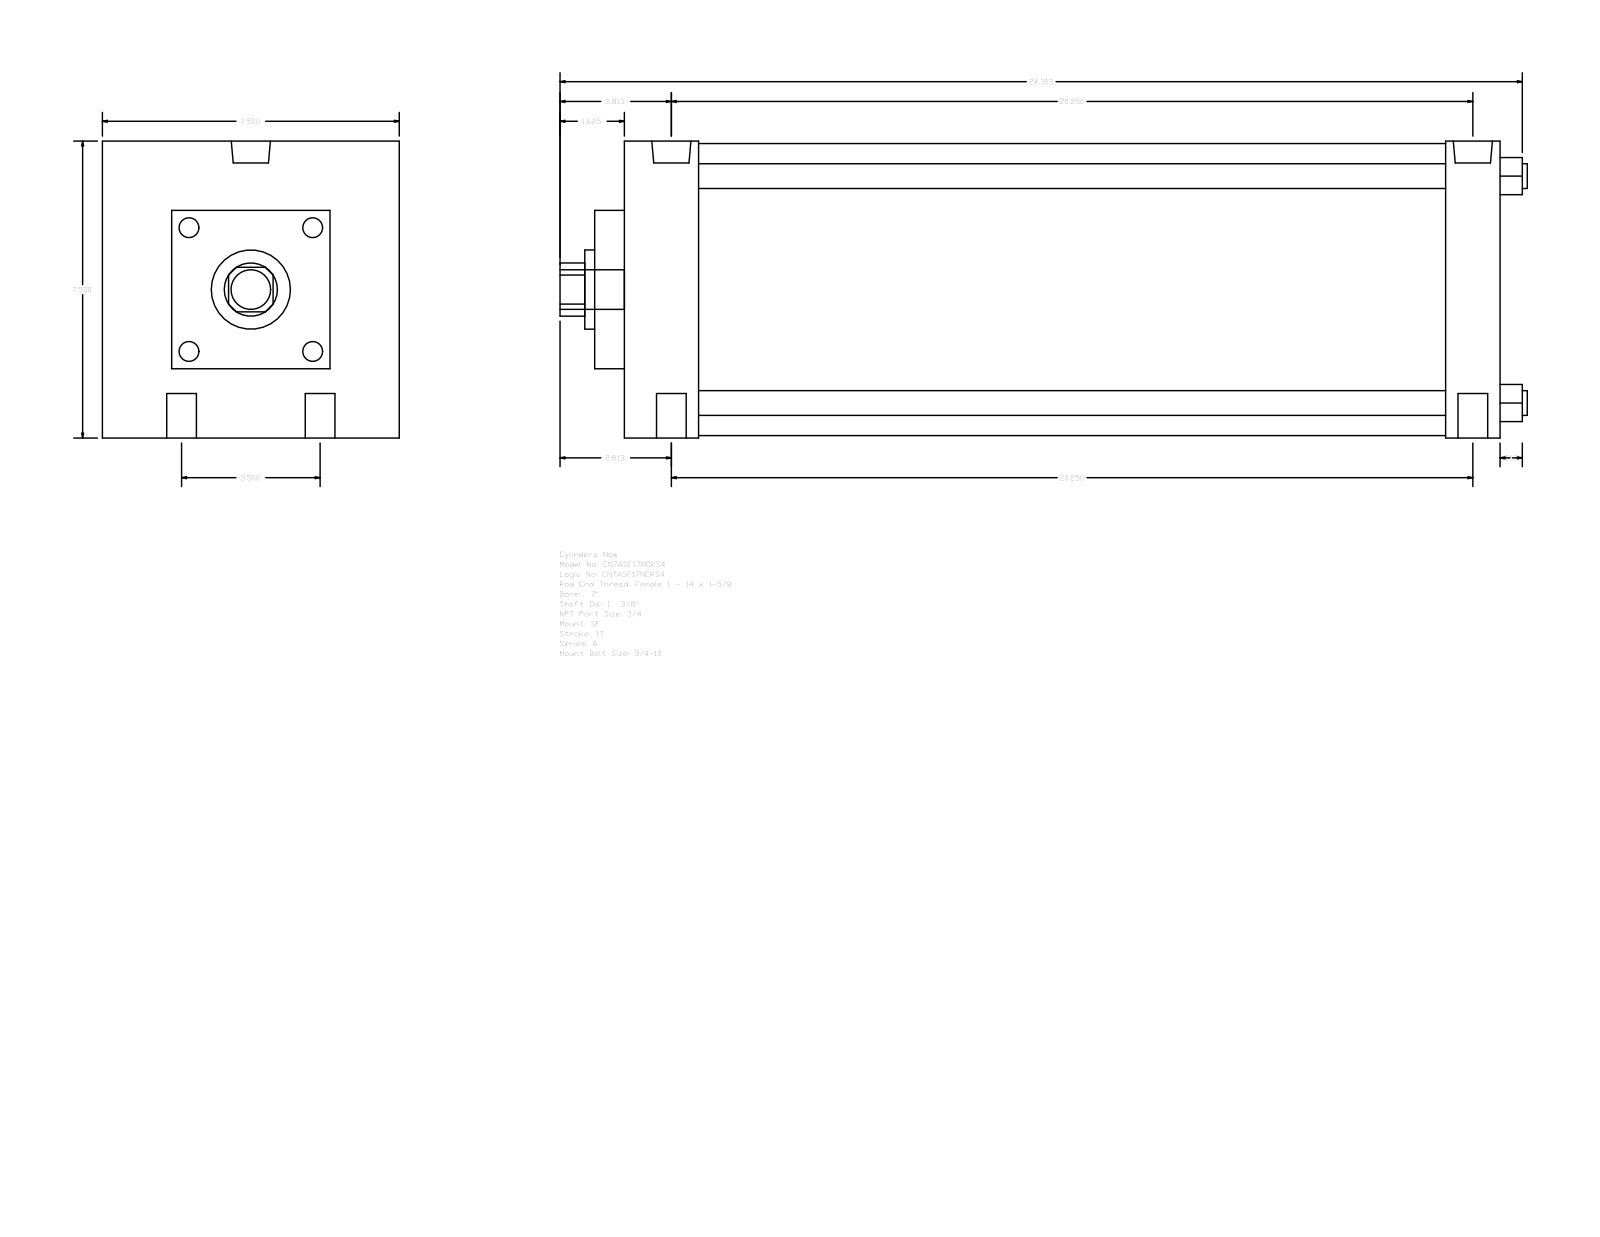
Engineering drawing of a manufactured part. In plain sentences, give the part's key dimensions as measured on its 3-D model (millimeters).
The part is named "A_SF__0700_1.375". Its 3-D file was written by "GSSL Pune (CONFIG_CONTROL_DESIGN)". It is 0 solids with 93 faces: 67 planar, 26 cylindrical and 0 other. Overall it measures 620.71 by 190.5 by 190.5 millimeters. Round holes: 4 of diameter 19.05, 2 of diameter 15.08, 2 of diameter 25.12, 1 of diameter 34.92, 1 of diameter 50.8. Round bosses or shafts: 4 of diameter 15.88, 1 of diameter 187.32, 1 of diameter 25.4. Partial cylindrical surfaces (rounded edges, fillets, slot ends): 1 of radius 17.06. The main face-to-face distances are 190.5, 561.98, 19.04, 581.02, 66.67, 546.1, 47.63, 527.06, 479.43, 514.35. The hole center spacings are 44.45, 516.27, 514.35, 88.9, 521.98, 503.23.
